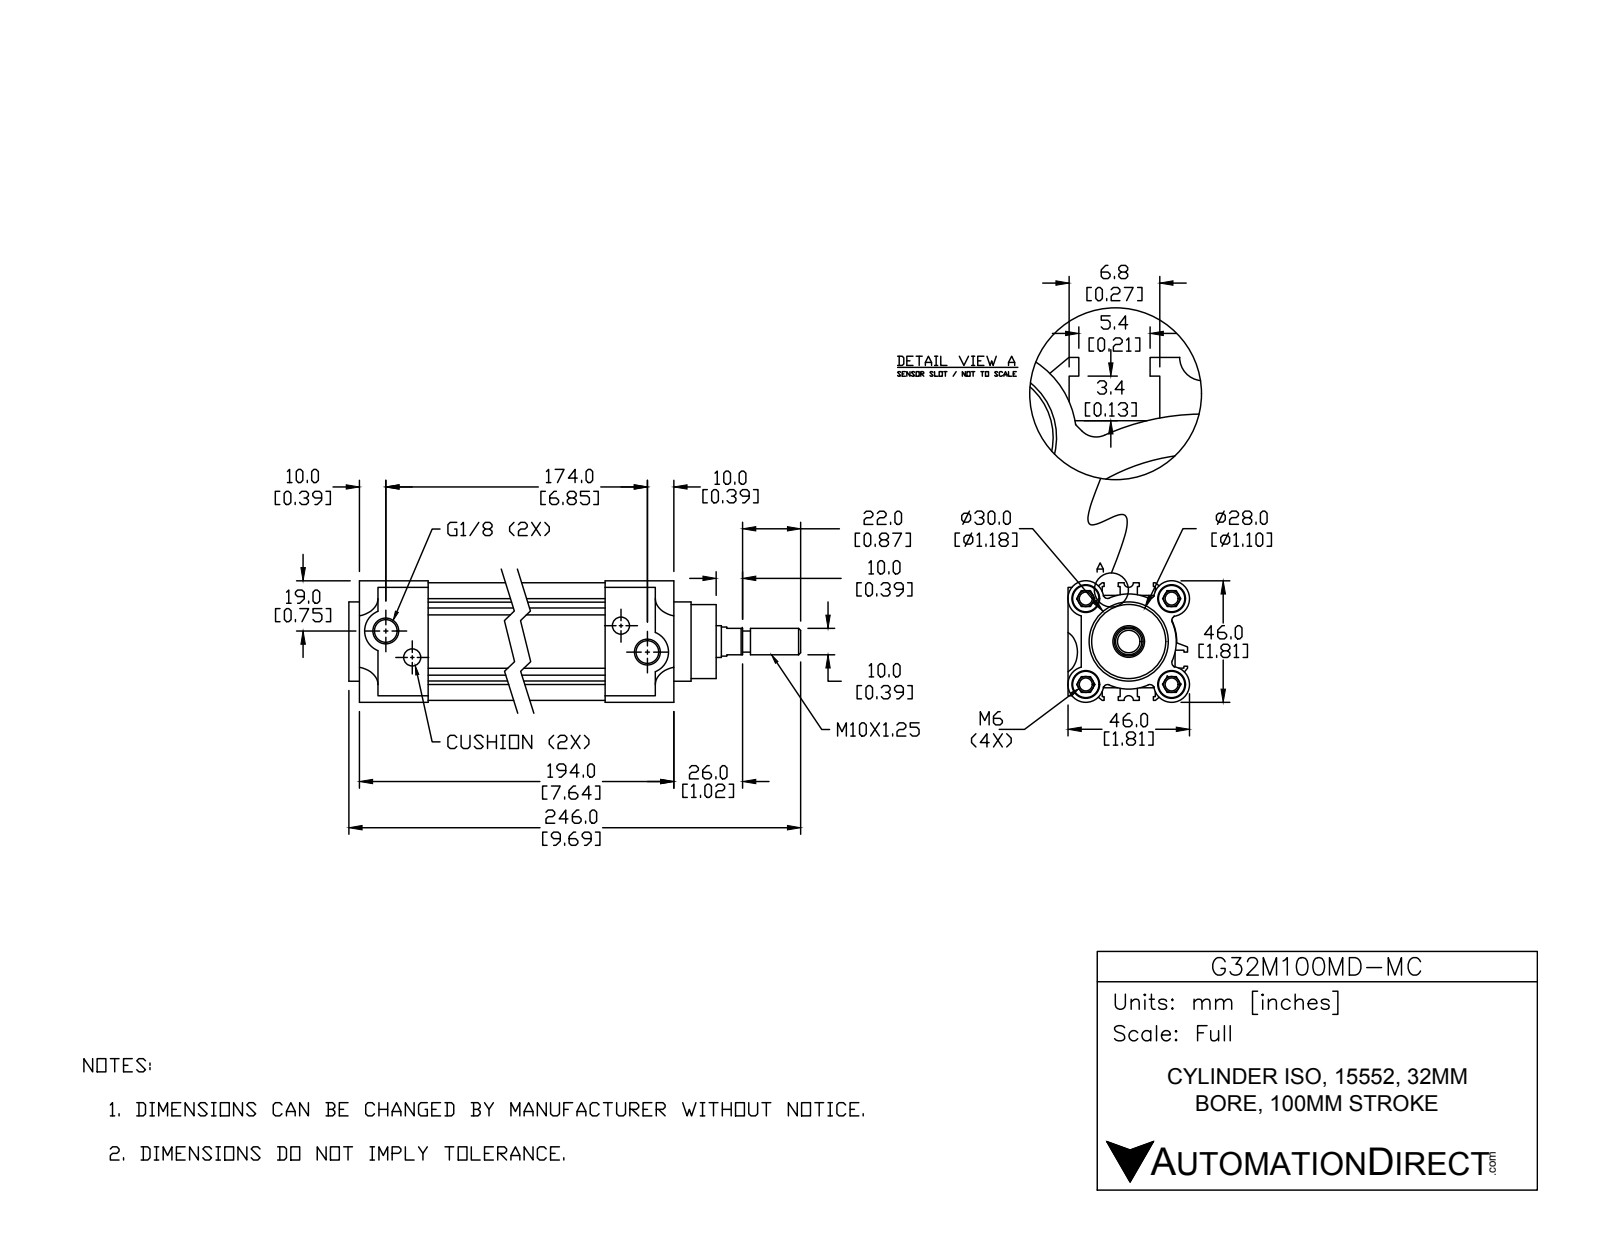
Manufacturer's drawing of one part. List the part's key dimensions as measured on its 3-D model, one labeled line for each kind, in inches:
Part name (STEP PRODUCT): 32-HL; 32-100-73.5-B; 32121-HR; 32121100-R (+1 more)
STEP written by: SolidWorks 2015 (CONFIG_CONTROL_DESIGN)
Units: inches
Bodies: 4 solids, 411 faces (229 planar, 138 cylindrical, 44 other)
Overall size (bounding box): 9.685 × 1.811 × 1.811
Volume: 16.33 in³ · Surface area: 151.1 in²
Round holes (diameter × count): ⌀0.194 ×4, ⌀0.413 ×4, ⌀0.256 ×2, ⌀0.337 ×2, ⌀0.472 ×1
Round bosses / shafts (diameter × count): ⌀0.394 ×5, ⌀1.26 ×1, ⌀1.181 ×1, ⌀1.102 ×1, ⌀0.433 ×1, ⌀0.315 ×1
Partial cylindrical surfaces — rounded edges, fillets, slot ends (radius × count): R0.004 ×12, R0.059 ×6, R0.236 ×4, R0.266 ×4, R0.069 ×2, R0.315 ×2, R0.709 ×1, R0.717 ×1
Main face-to-face distances: 1.565, 0.187, 1.004, 1.378, 0.276, 0.268, 5.315, 0.748, 0.48, 1.272
Hole centre spacings: 0.905, 1.28, 0.557, 1.809, 6.457, 6.081, 6.857
